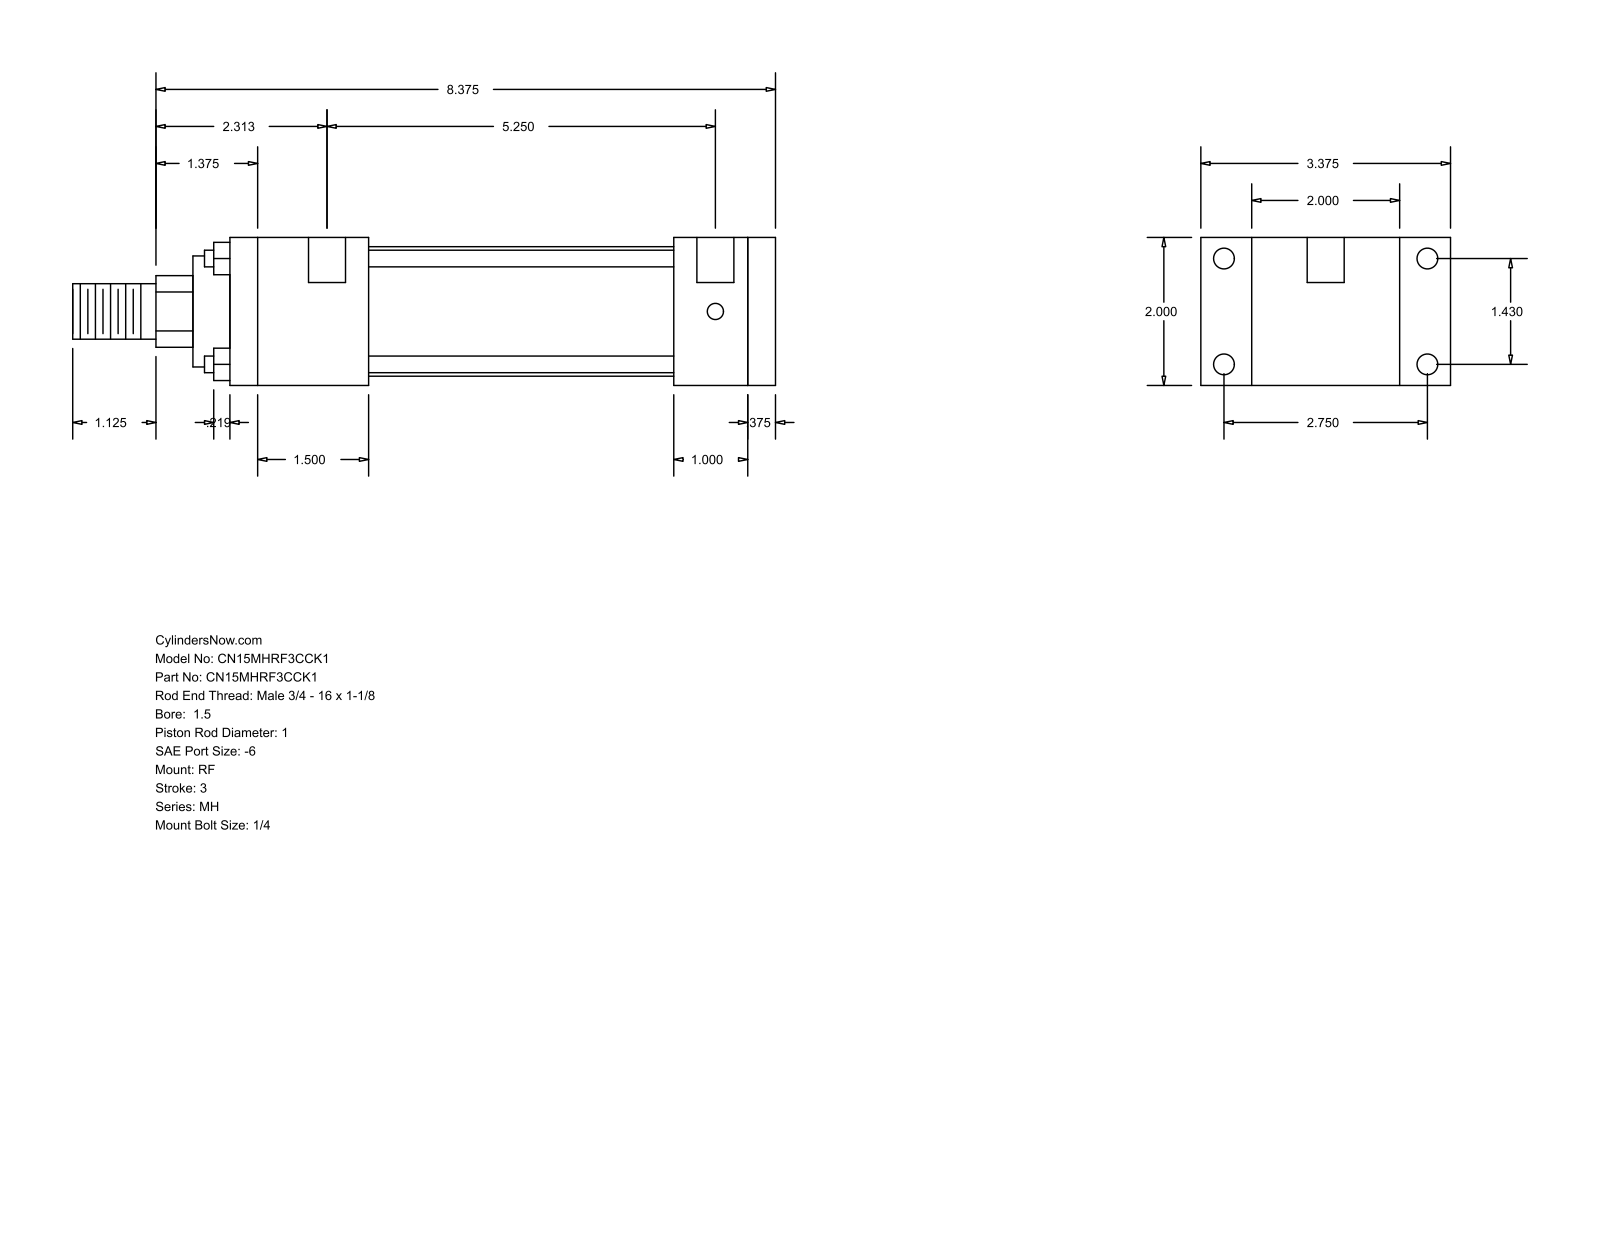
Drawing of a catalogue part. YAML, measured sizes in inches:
part_name: "MH_RF__0150_1"
step_written_by: "GSSL Pune (CONFIG_CONTROL_DESIGN)"
units: inches
bodies: {solids: 0, faces: 92, planar: 64, cylindrical: 28, other: 0}
overall_size: [9.5, 3.375, 2]
round_holes:
  - {diameter: 0.219, count: 4}
  - {diameter: 0.281, count: 4}
  - {diameter: 0.5, count: 2}
round_bosses_or_shafts:
  - {diameter: 0.225, count: 4}
  - {diameter: 1.75, count: 1}
  - {diameter: 1.5, count: 1}
  - {diameter: 1, count: 1}
  - {diameter: 0.75, count: 1}
partial_cylinders:
  - {radius: 0.484, count: 1}
face_to_face_distances: [2, 0.375, 7, 1, 7.375, 0.687, 2.687, 6, 1.375, 1.875]
hole_center_spacings: [1.43, 2.75, 3.099, 5.375, 0.125, 5.25]
